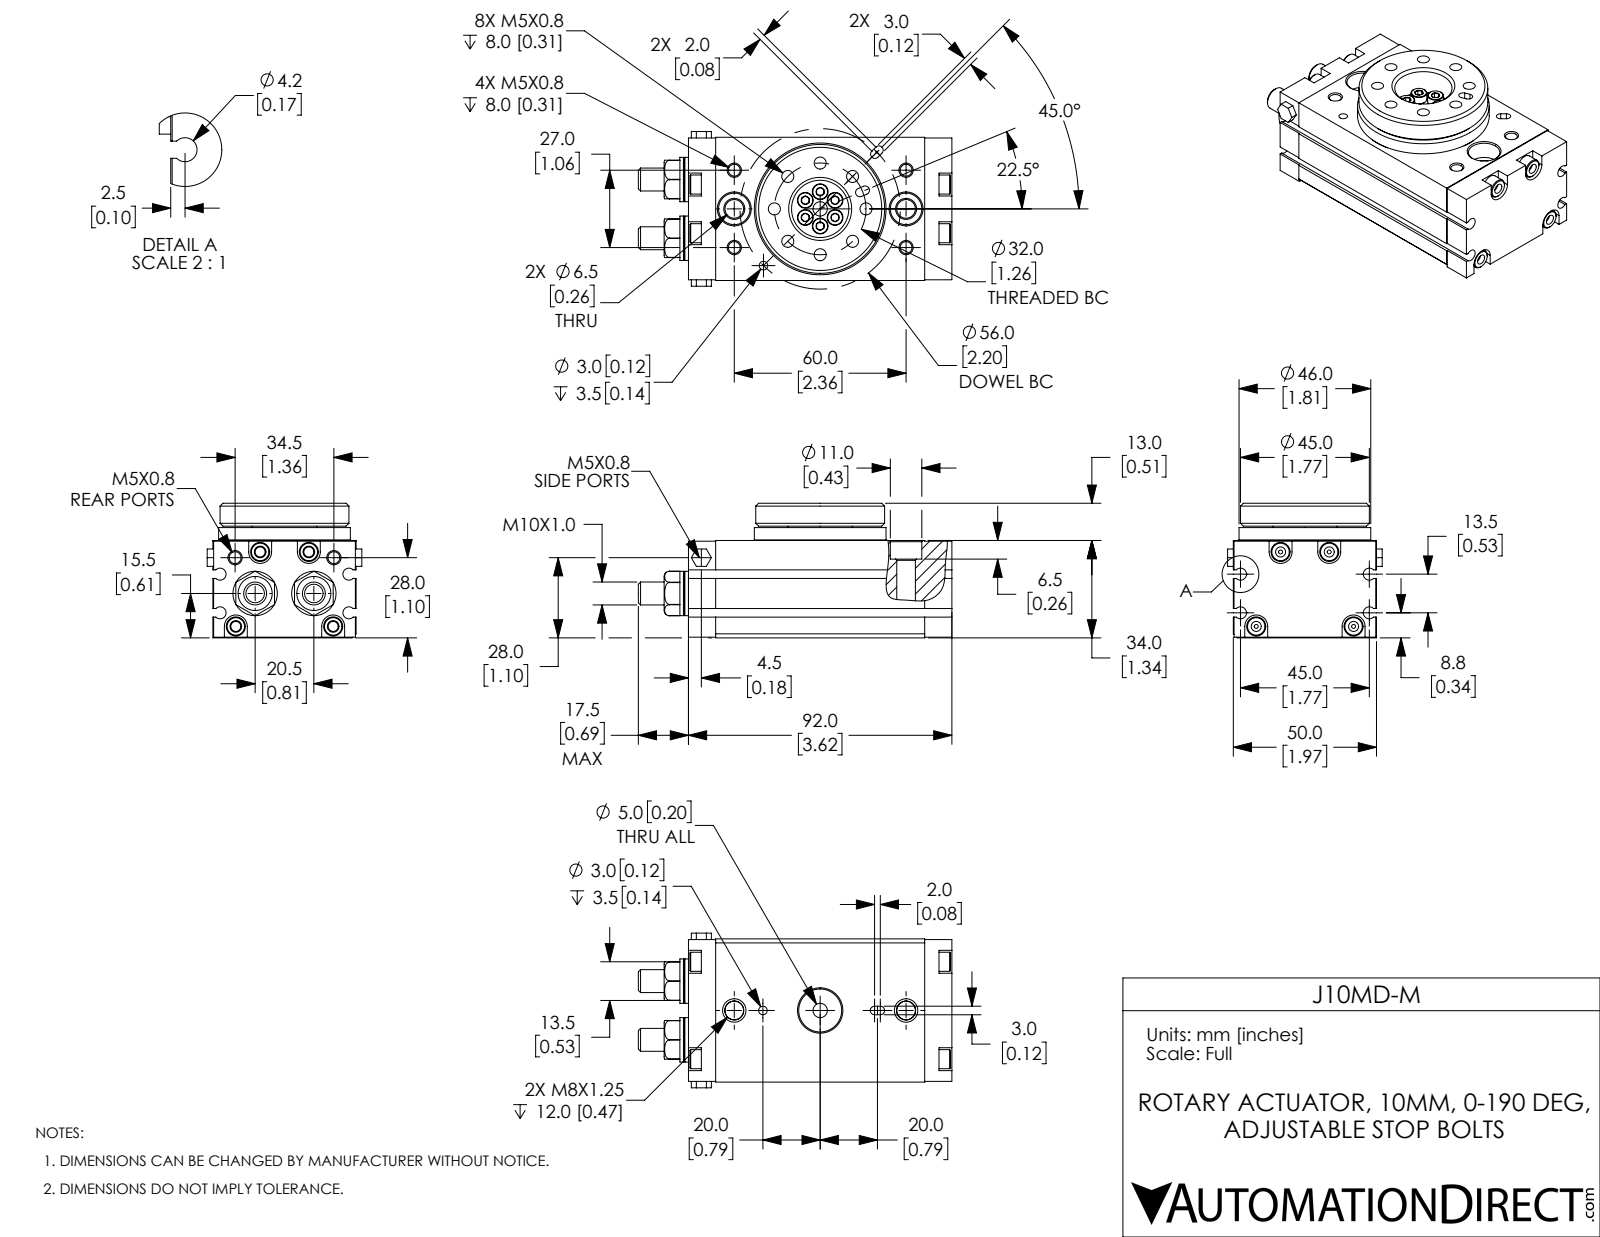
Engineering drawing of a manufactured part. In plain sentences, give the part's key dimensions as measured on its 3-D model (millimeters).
The part is named "J10MD-M_M3_91290A109; J10MD-M; J10MD-M_BODY; J10MD-M_table". Its 3-D file was written by "SolidWorks 2017 (AUTOMOTIVE_DESIGN)". It is 8 solids with 761 faces: 211 planar, 342 cylindrical and 208 other. Overall it measures 109.5 by 54 by 47 millimeters. Its volume is 163 167 cubic millimeters and its surface area 35 782 square millimeters. Round holes: 8 of diameter 4.2, 6 of diameter 4.13, 4 of diameter 3.5, 2 of diameter 3, 2 of diameter 6.5, 2 of diameter 6.65, 2 of diameter 11, 1 of diameter 5, 1 of diameter 15, 1 of diameter 20, 1 of diameter 23. Round bosses or shafts: 6 of diameter 5.5, 6 of diameter 3, 6 of diameter 2.35, 4 of diameter 6.66, 2 of diameter 15.5, 2 of diameter 8, 1 of diameter 46, 1 of diameter 45. Partial cylindrical surfaces (rounded edges, fillets, slot ends): 6 of radius 1.5, 4 of radius 2.1, 4 of radius 4. The main face-to-face distances are 34, 50, 4.5, 8, 33.75, 3, 13, 38.5, 8.5, 13.25. The hole center spacings are 12.24, 29.56, 34, 13.5, 15.99, 16, 18.82, 19.45.
